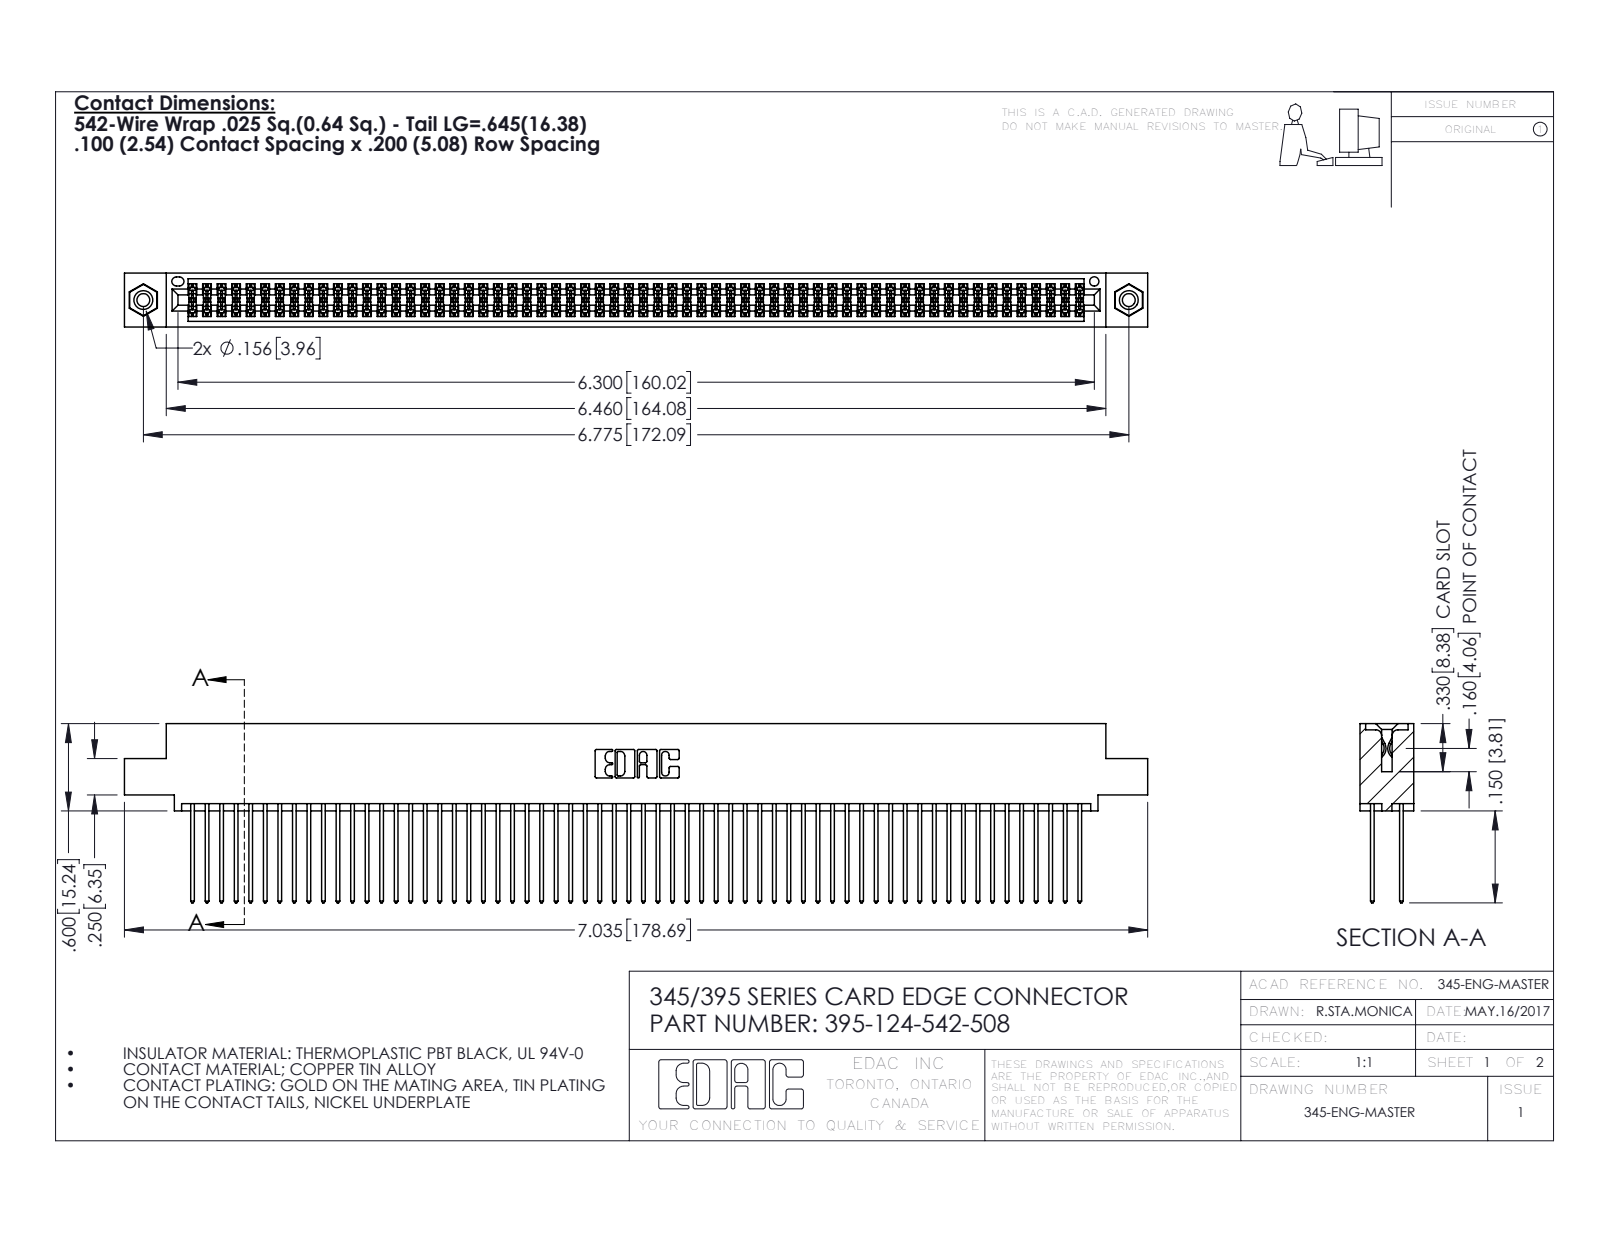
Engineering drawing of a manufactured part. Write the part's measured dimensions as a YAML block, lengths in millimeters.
part_name: "345-292-001_345-293-142; 345-250-001_345-250-003-102; 345 Part_0.110 Offset - 0.156 Dia-TI; 395-124-542-508"
step_written_by: "SolidWorks 2016 (CONFIG_CONTROL_DESIGN)"
units: millimeters
bodies: {solids: 127, faces: 6390, planar: 4208, cylindrical: 2166, other: 16}
overall_size: [178.7, 31.3, 9.4]
volume: 18040
surface_area: 29860
round_holes:
  - {diameter: 2.3, count: 2}
  - {diameter: 3.2, count: 2}
  - {diameter: 4, count: 2}
  - {diameter: 1.6, count: 1}
round_bosses_or_shafts:
  - {diameter: 3.9, count: 2}
partial_cylinders:
  - {radius: 0.2, count: 186}
  - {radius: 0.3, count: 124}
  - {radius: 0.3, count: 22}
  - {radius: 0.2, count: 6}
  - {radius: 0.8, count: 6}
  - {radius: 0.7, count: 3}
  - {radius: 0.4, count: 2}
  - {radius: 0.5, count: 2}
face_to_face_distances: [1.8, 7.6, 5.1, 2.5, 6.9, 0.6, 5.7, 9.4, 4.4, 3.8]
hole_center_spacings: [6.9, 166.1, 172.1]
